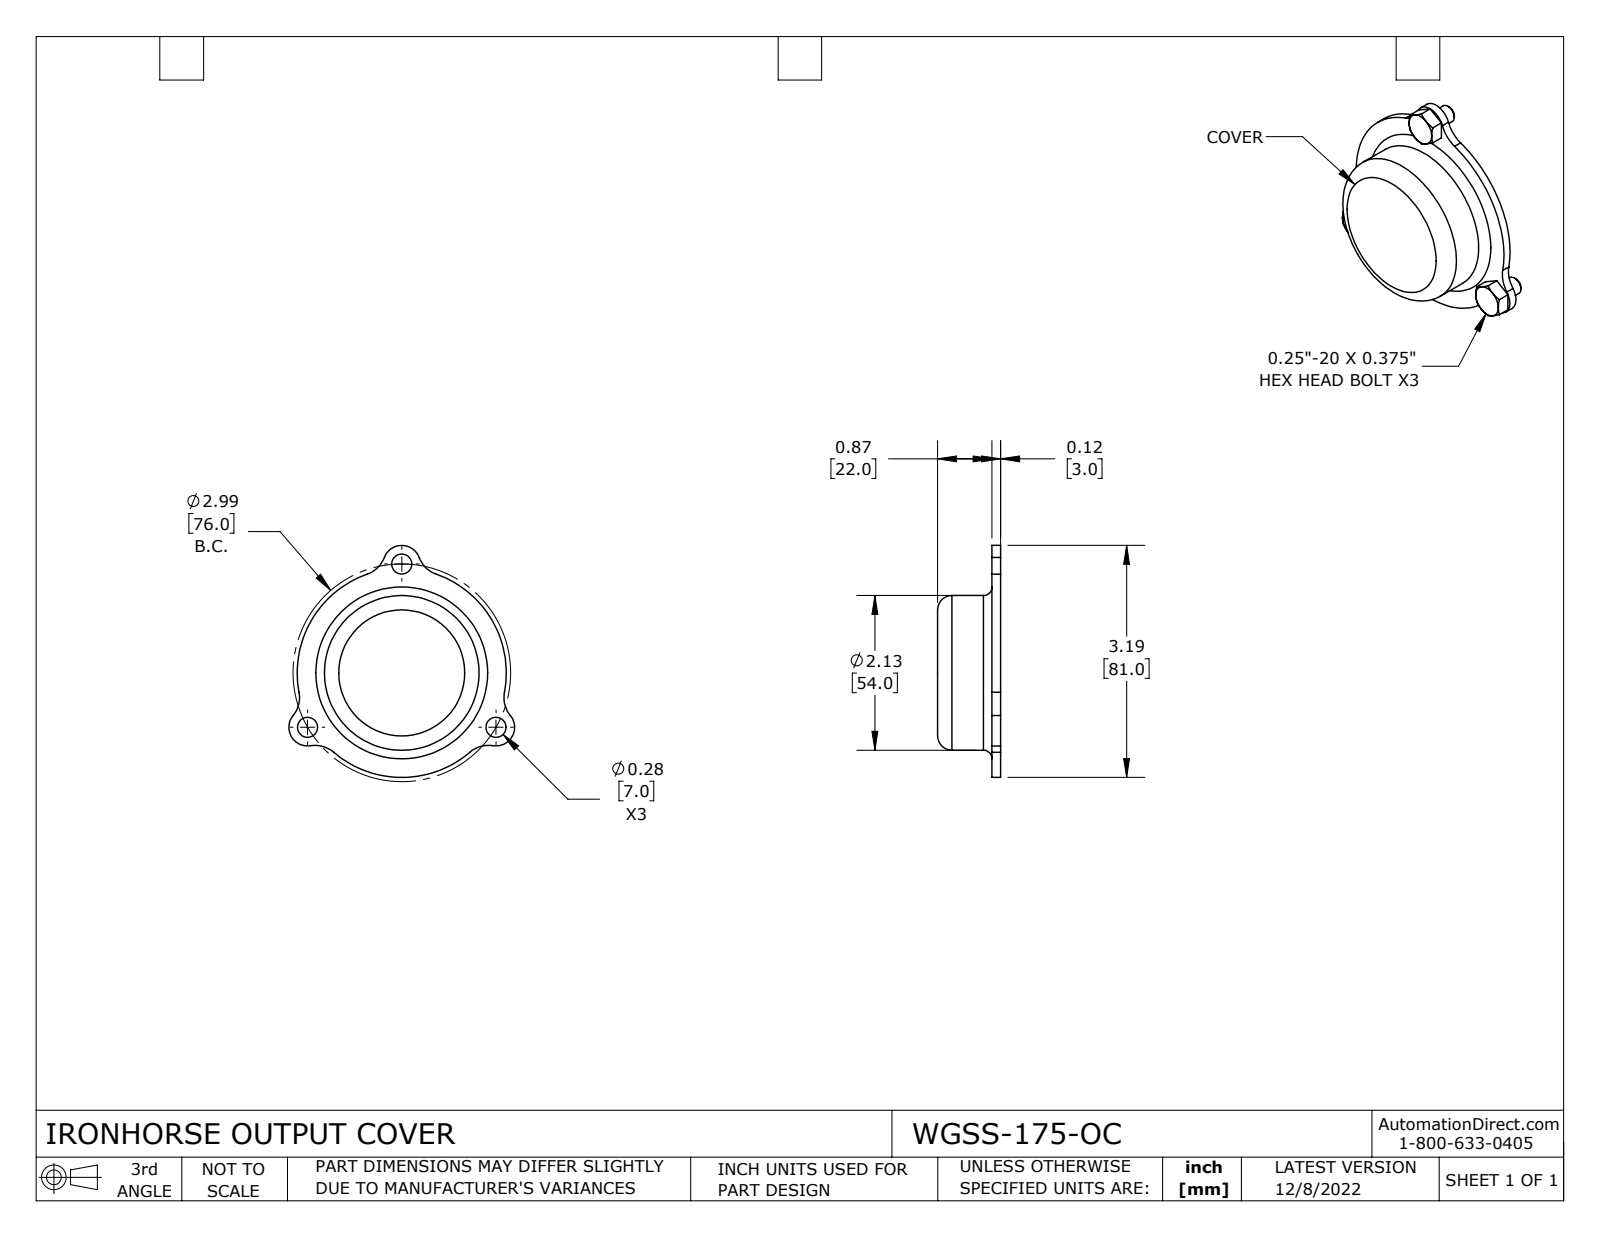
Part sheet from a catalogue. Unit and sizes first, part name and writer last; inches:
Units: inches
Overall size (bounding box): 3.189 × 3.103 × 1.123
Round holes (diameter × count): ⌀0.276 ×3, ⌀1.969 ×1
Round bosses / shafts (diameter × count): ⌀0.25 ×3, ⌀2.126 ×1
Partial cylindrical surfaces — rounded edges, fillets, slot ends (radius × count): R0.394 ×6, R0.256 ×3, R1.437 ×1
Main face-to-face distances: 0.118, 0.866, 0.748, 0.787, 0.669, 0.079, 1.296, 0.306, 0.188, 0.481
Hole centre spacings: 1.496, 2.591
Volume: 1.138 in³ · Surface area: 25.83 in²
Bodies: 4 solids, 94 faces (31 planar, 31 cylindrical, 32 other)
Part name (STEP PRODUCT): WGSS-175-OC
STEP written by: SolidWorks 2021 (CONFIG_CONTROL_DESIGN)
